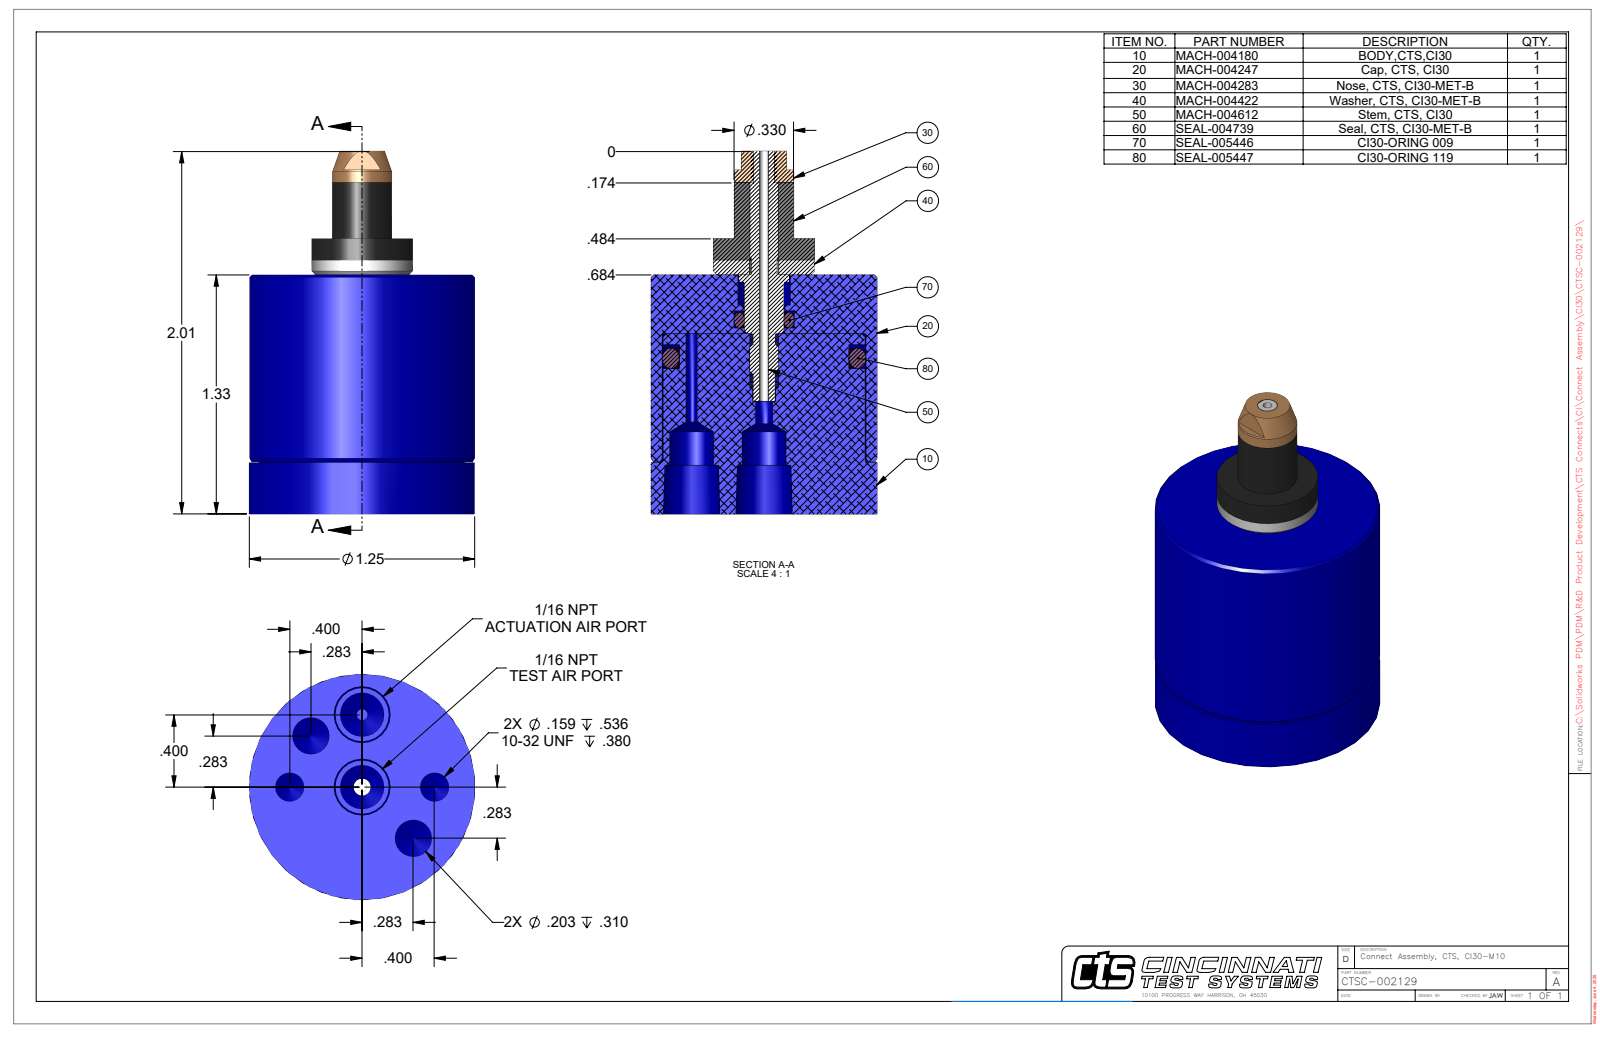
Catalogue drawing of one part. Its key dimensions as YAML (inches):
part_name: "CTSC-002129"
step_written_by: "SolidWorks 2023 (AUTOMOTIVE_DESIGN)"
units: inches
bodies: {solids: 2, faces: 90, planar: 22, cylindrical: 36, other: 32}
overall_size: [2.009, 1.25, 1.25]
volume: 1.601
surface_area: 13.23
round_holes:
  - {diameter: 0.159, count: 2}
  - {diameter: 0.203, count: 2}
  - {diameter: 0.242, count: 2}
  - {diameter: 0.052, count: 1}
  - {diameter: 0.062, count: 1}
  - {diameter: 0.094, count: 1}
  - {diameter: 0.113, count: 1}
  - {diameter: 0.289, count: 1}
  - {diameter: 1.125, count: 1}
round_bosses_or_shafts:
  - {diameter: 1.25, count: 1}
  - {diameter: 1.115, count: 1}
  - {diameter: 0.56, count: 1}
  - {diameter: 0.33, count: 1}
  - {diameter: 0.277, count: 1}
face_to_face_distances: [1.325, 0.287, 1.039, 1.525, 1.239, 0.2, 0.29, 1.035, 1.235, 2.009]
hole_center_spacings: [0.306, 0.4, 0.739, 0.4, 0.566, 0.8, 0.8]
